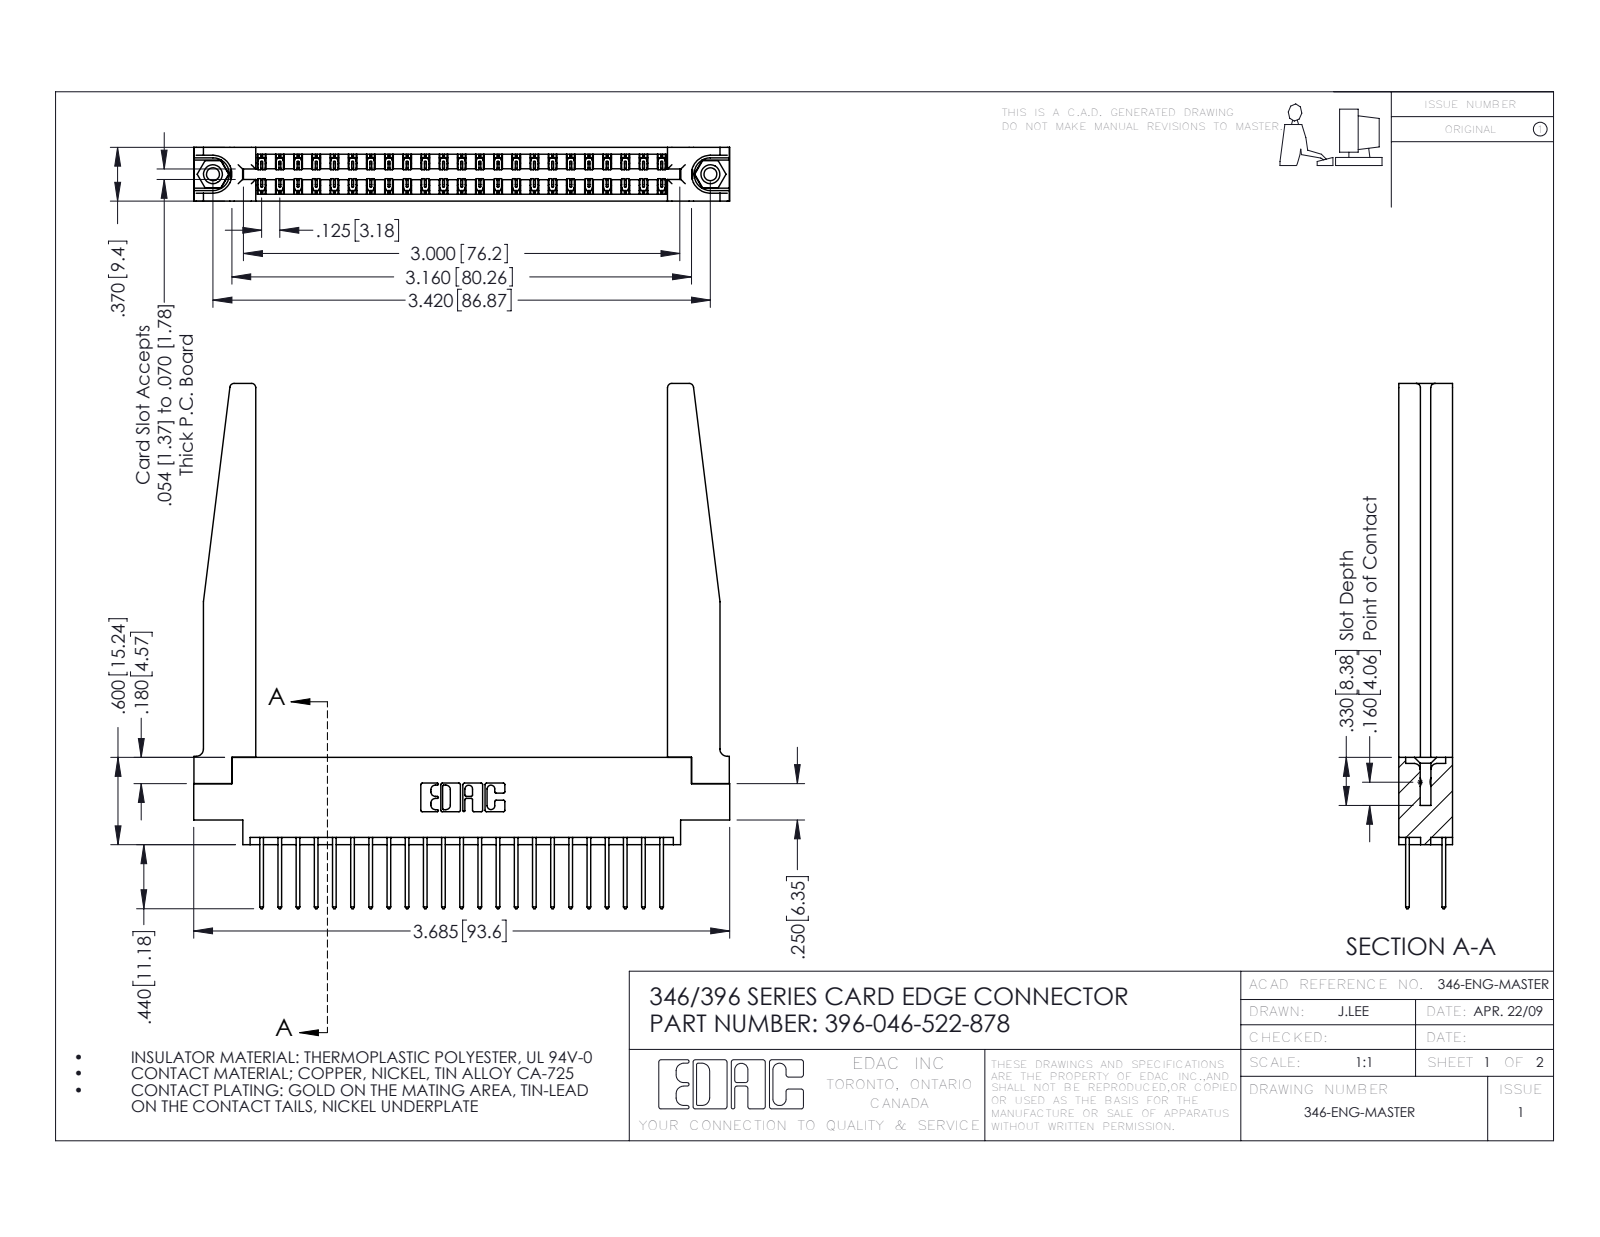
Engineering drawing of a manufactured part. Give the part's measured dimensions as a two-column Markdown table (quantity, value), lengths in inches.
| quantity | value |
| --- | --- |
| part name | 396-046-522-878; 345-292-001_345-293-122; 346 Part_0.170 Offset - 0.156 Dia-TH; 346-220-078_345-220-078 (+1 more) |
| STEP written by | SolidWorks 2016 (CONFIG_CONTROL_DESIGN) |
| units | inches |
| bodies | 51 solids, 2752 faces (1832 planar, 868 cylindrical, 52 other) |
| overall size | 3.685 × 3.61 × 0.37 |
| volume | 0.967 in³ |
| surface area | 29.85 in² |
| round holes (diameter × count) | 0.089 × 2, 0.125 × 2, 0.156 × 2, 0.064 × 1 |
| round bosses / shafts (diameter × count) | 0.155 × 2 |
| partial cylindrical surfaces (radius × count) | 0.006 × 69, 0.01 × 46, 0.01 × 22, 0.03 × 8, 0.007 × 6, 0.031 × 6, 0.026 × 3, 0.014 × 2 |
| main face-to-face distances | 0.37, 0.048, 0.322, 0.072, 0.25, 0.148, 0.15, 0.298, 0.025, 0.275 |
| hole center spacings | 0.246, 3.212, 3.42 |
